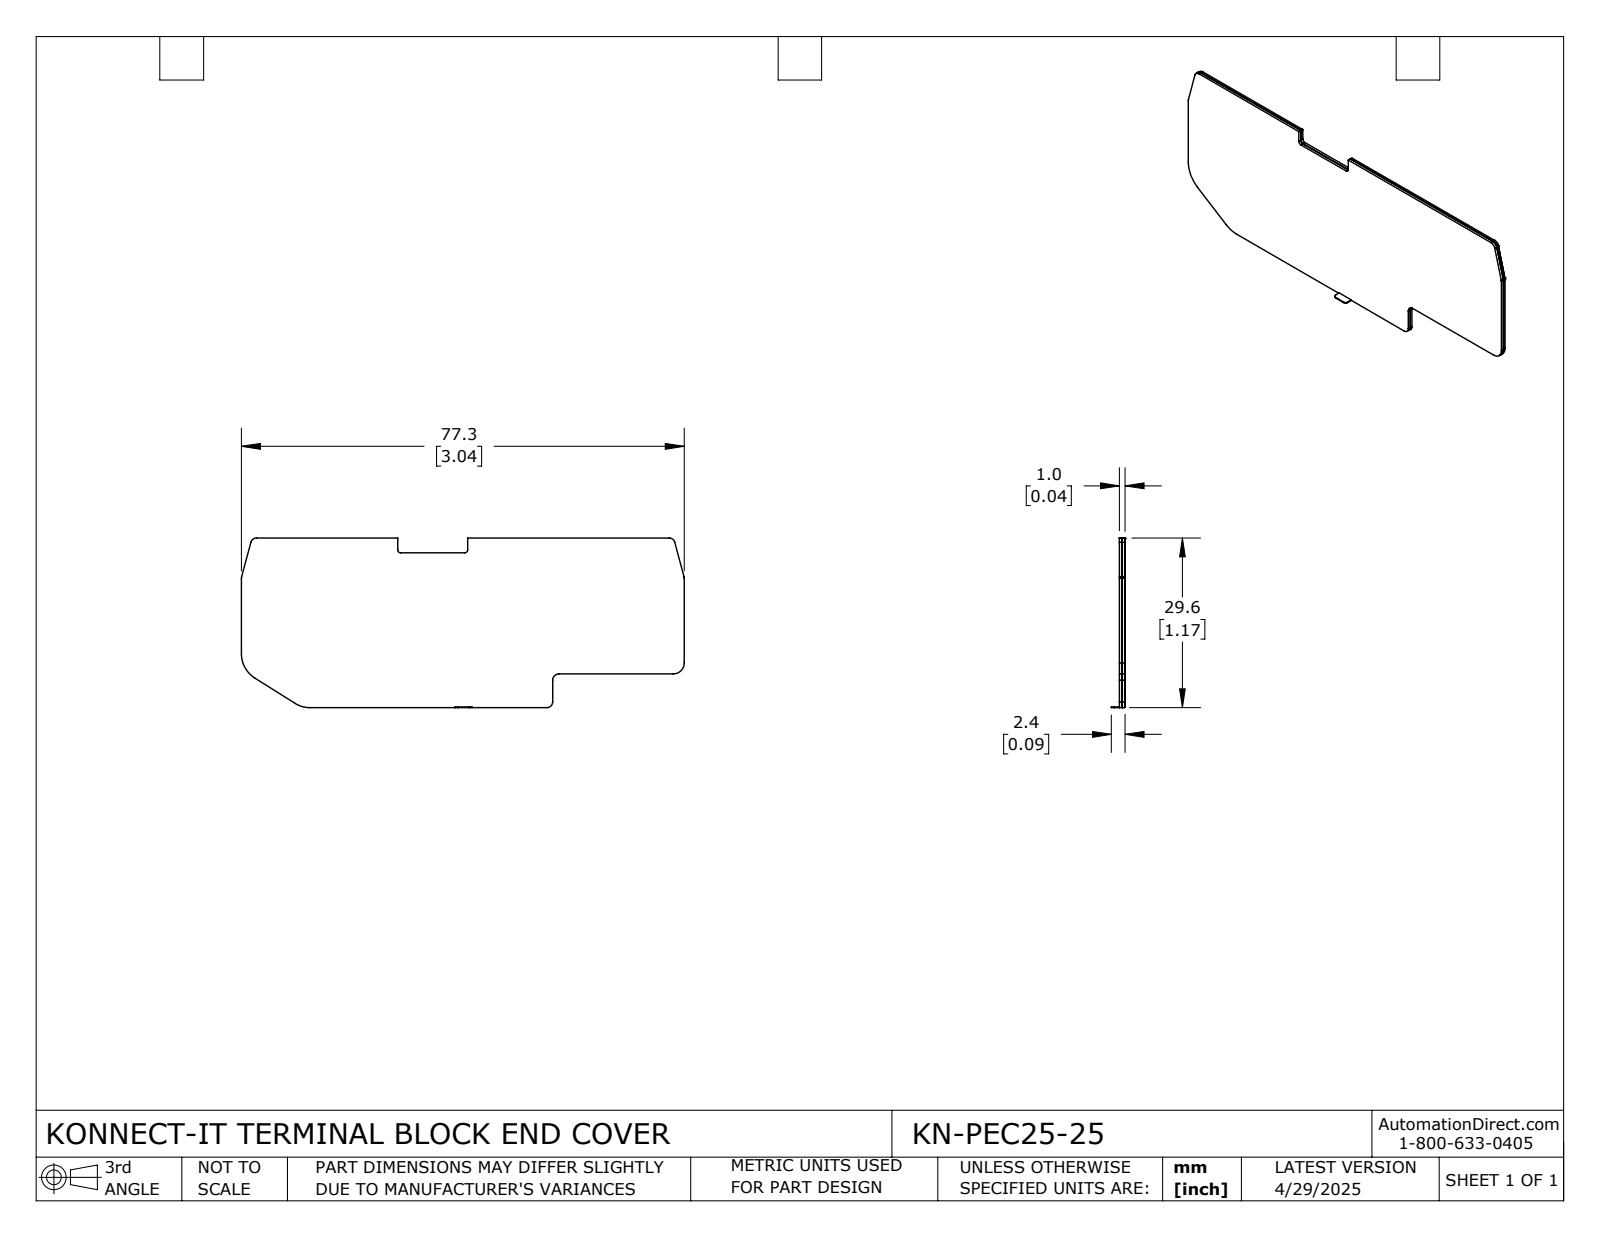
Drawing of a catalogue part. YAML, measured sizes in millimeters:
part_name: "KN-PEC25-25"
step_written_by: "SolidWorks 2024 (CONFIG_CONTROL_DESIGN)"
units: millimeters
bodies: {solids: 2, faces: 78, planar: 45, cylindrical: 33, other: 0}
overall_size: [77.31, 29.61, 2.4]
volume: 2071
surface_area: 8505
partial_cylinders:
  - {radius: 0.9, count: 5}
  - {radius: 1, count: 5}
  - {radius: 0.5, count: 4}
  - {radius: 4.8, count: 2}
  - {radius: 4.9, count: 2}
  - {radius: 1.1, count: 1}
  - {radius: 1.2, count: 1}
  - {radius: 1.8, count: 1}
face_to_face_distances: [0.5, 1, 29.61, 5.89, 0.9, 0.4, 23.72, 29.51, 77.31, 27.02]
